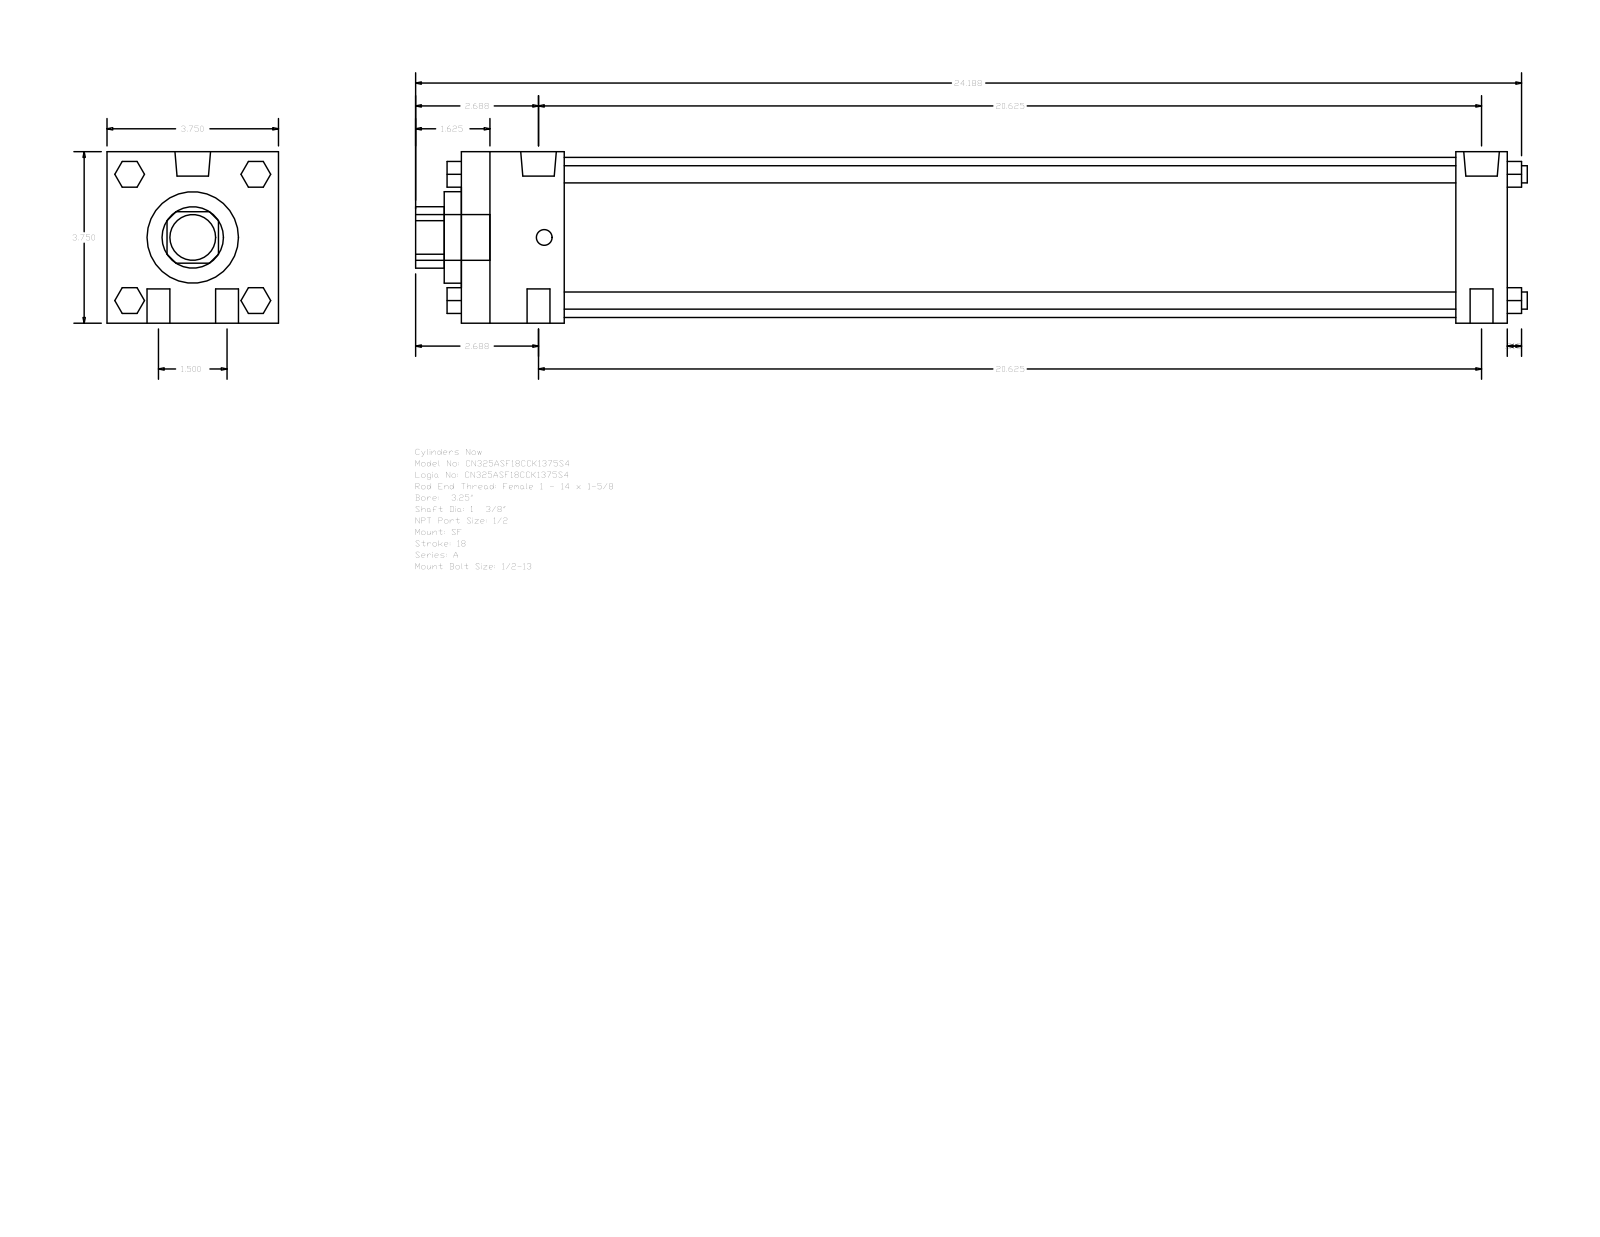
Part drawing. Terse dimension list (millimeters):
name: A_SF__0325_1.375
written by: GSSL Pune (CONFIG_CONTROL_DESIGN)
unit: mm
bodies: 0 solids, 124 faces (94 planar, 30 cylindrical, 0 other)
size: 617.54 × 95.25 × 95.25
holes: 1× ⌀34.92, 1× ⌀50.8, 1× ⌀88.9
bosses: 4× ⌀12.7, 4× ⌀9.53, 2× ⌀19.77, 2× ⌀8.73, 1× ⌀25.4
rounds: 1× R17.06
face distances: 95.24, 581.02, 28.57, 552.45, 57.15, 495.3, 523.87, 9.52, 66.67, 561.97
